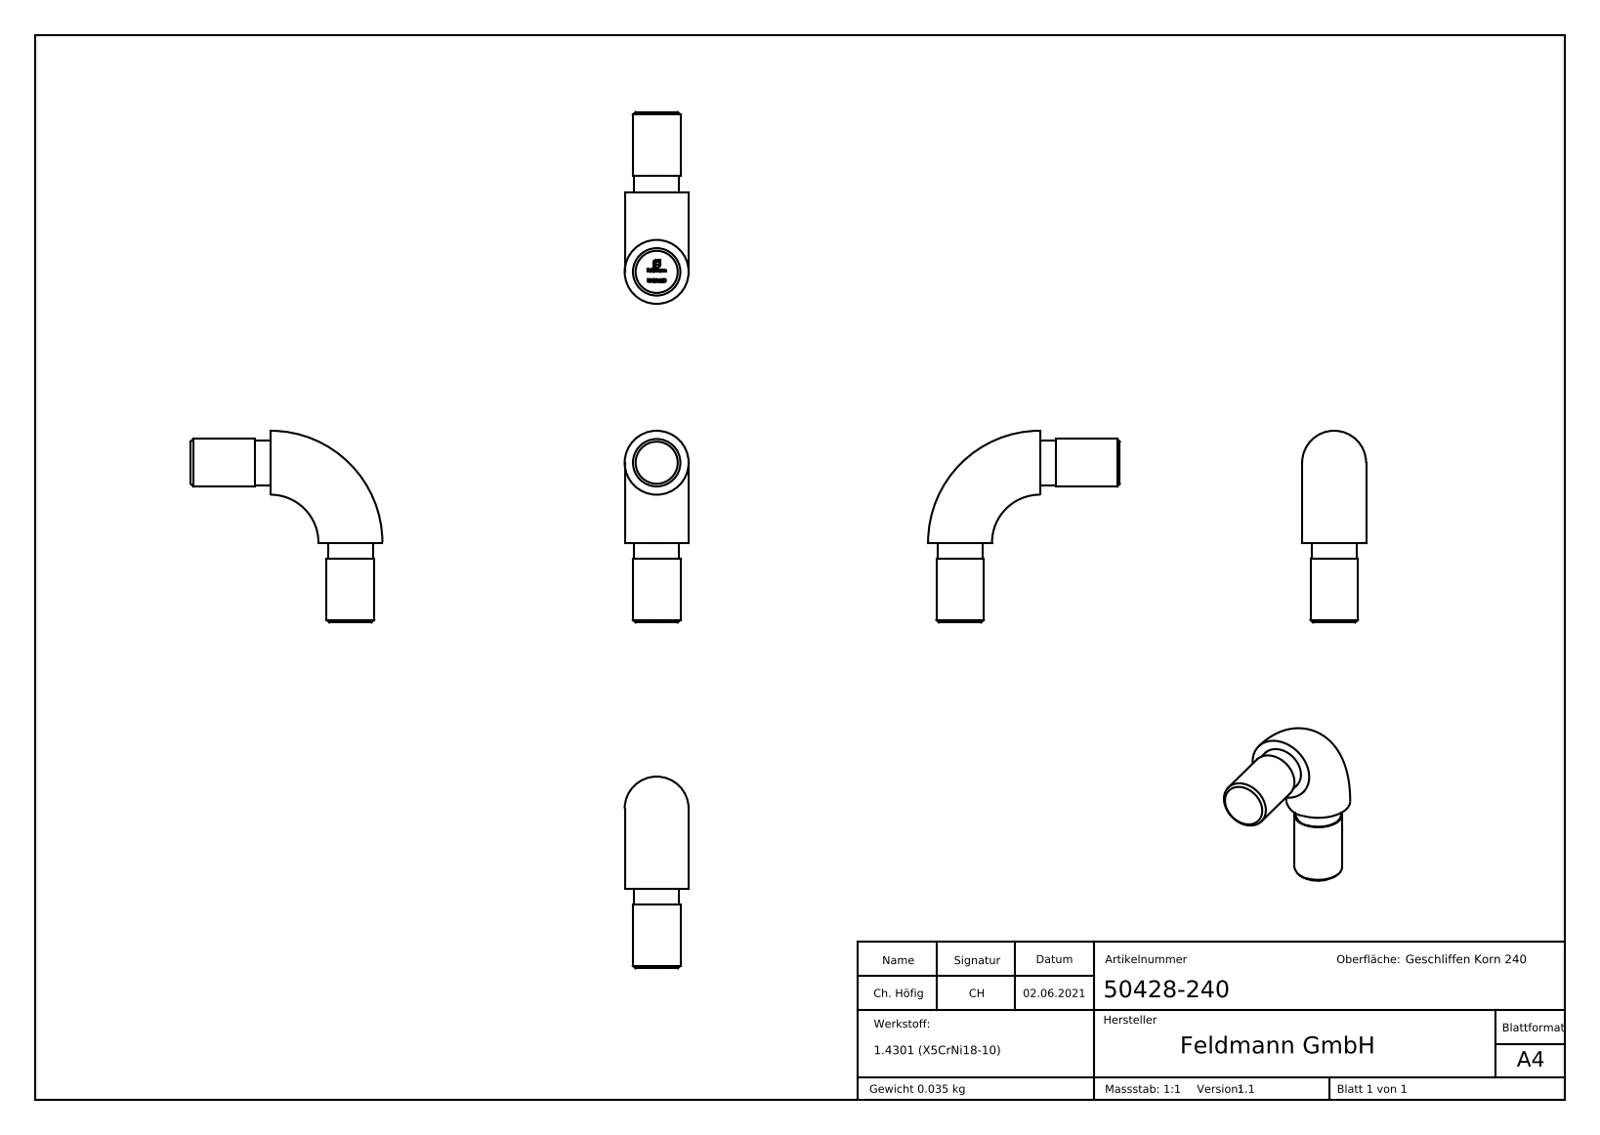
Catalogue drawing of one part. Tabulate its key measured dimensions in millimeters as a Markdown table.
| quantity | value |
| --- | --- |
| part name | 50428-240 |
| STEP written by | SolidWorks 2018 (CONFIG_CONTROL_DESIGN) |
| units | millimeters |
| bodies | 1 solid, 294 faces (157 planar, 8 cylindrical, 129 other) |
| overall size | 36 × 36 × 12 |
| volume | 4 491 mm³ |
| surface area | 1 956 mm² |
| round bosses / shafts (diameter × count) | 8.9 × 2, 8.5 × 2 |
| main face-to-face distances | 15, 12, 3, 11.9, 14.9, 1.1, 0.81, 1.46, 0.47, 0.73 |
